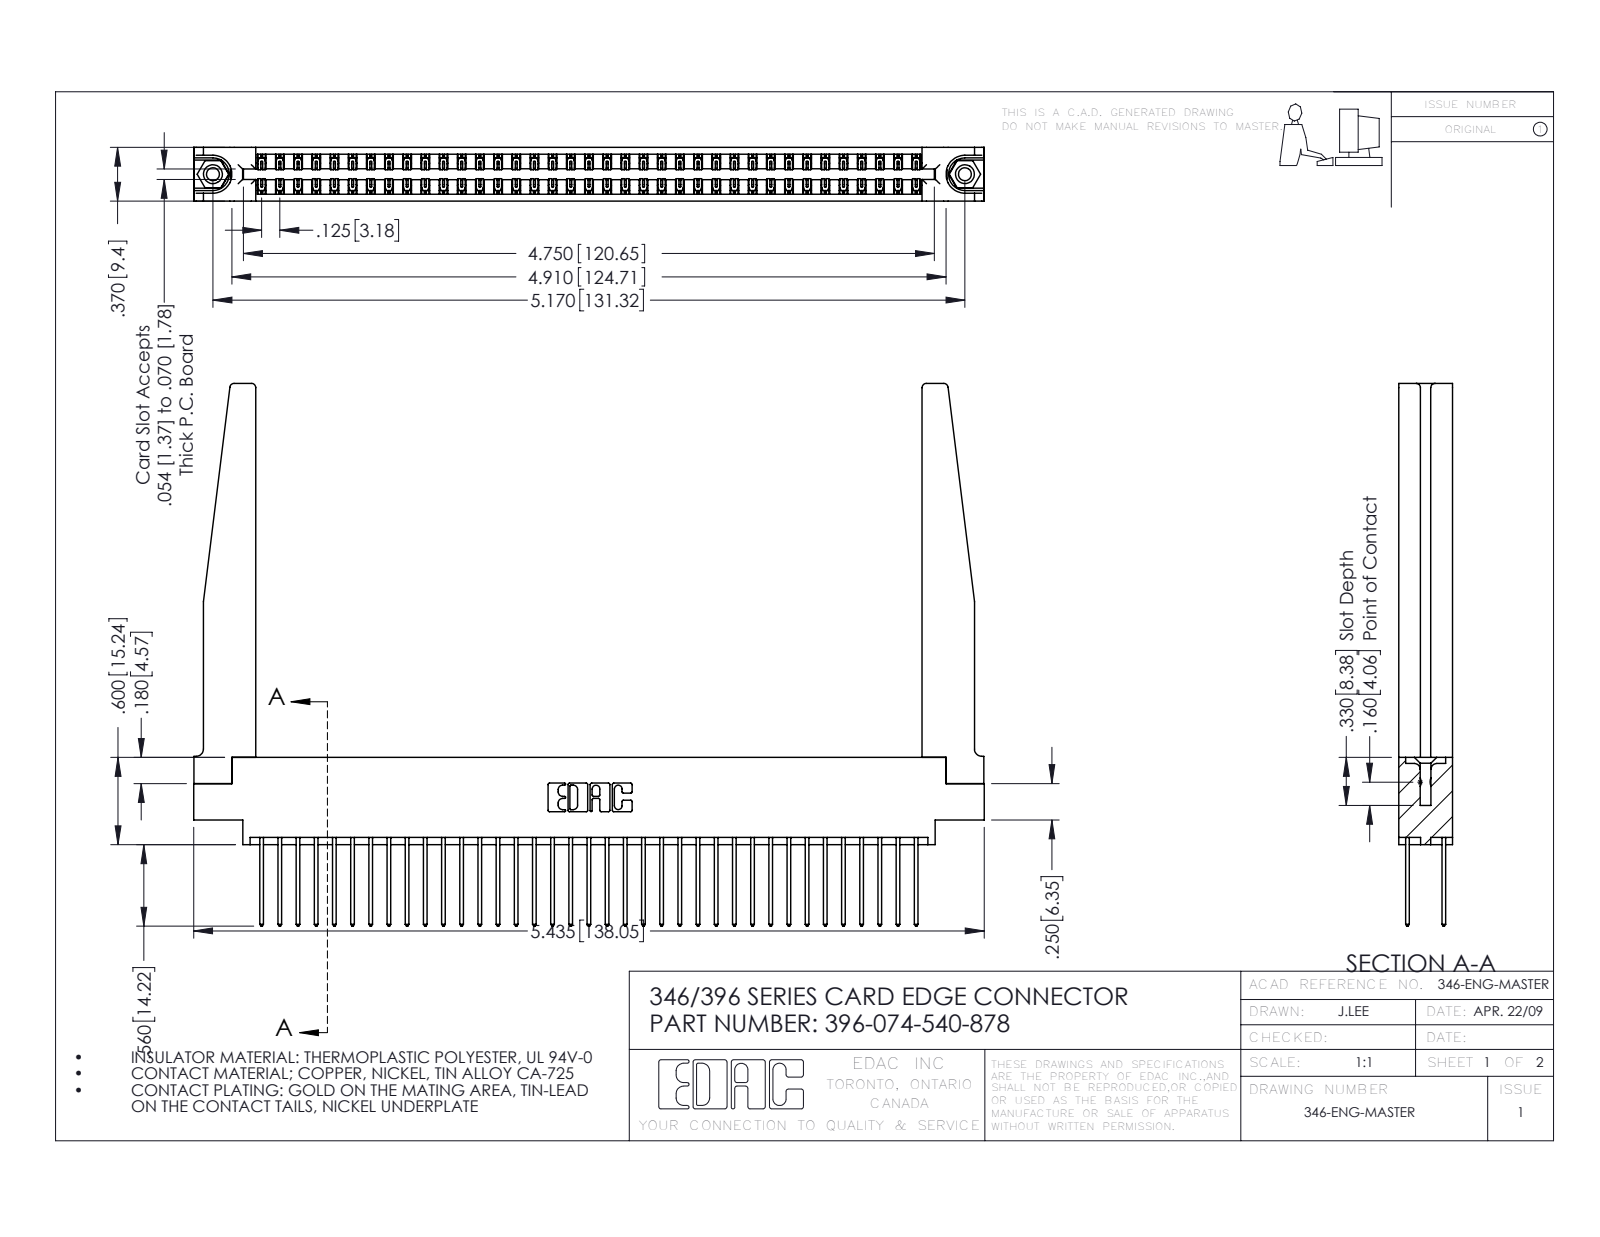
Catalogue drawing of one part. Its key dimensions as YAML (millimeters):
part_name: "345-250-001_345-250-001-102; 346 Part_0.170 Offset - 0.156 Dia-TH; 345-292-001_345-293-140; 396-074-540-878 (+1 more)"
step_written_by: "SolidWorks 2016 (CONFIG_CONTROL_DESIGN)"
units: millimeters
bodies: {solids: 79, faces: 4208, planar: 2812, cylindrical: 1344, other: 52}
overall_size: [138, 94.7, 9.4]
volume: 20450
surface_area: 26590
round_holes:
  - {diameter: 2.3, count: 2}
  - {diameter: 3.2, count: 2}
  - {diameter: 4, count: 2}
  - {diameter: 1.6, count: 1}
round_bosses_or_shafts:
  - {diameter: 3.9, count: 2}
partial_cylinders:
  - {radius: 0.2, count: 111}
  - {radius: 0.3, count: 74}
  - {radius: 0.3, count: 22}
  - {radius: 0.8, count: 8}
  - {radius: 0.2, count: 6}
  - {radius: 0.8, count: 6}
  - {radius: 0.7, count: 3}
  - {radius: 0.4, count: 2}
face_to_face_distances: [1.2, 8.2, 9.4, 1.8, 6.4, 7.6, 0.6, 3.8, 3.8, 7]
hole_center_spacings: [6.2, 126, 131.3]
